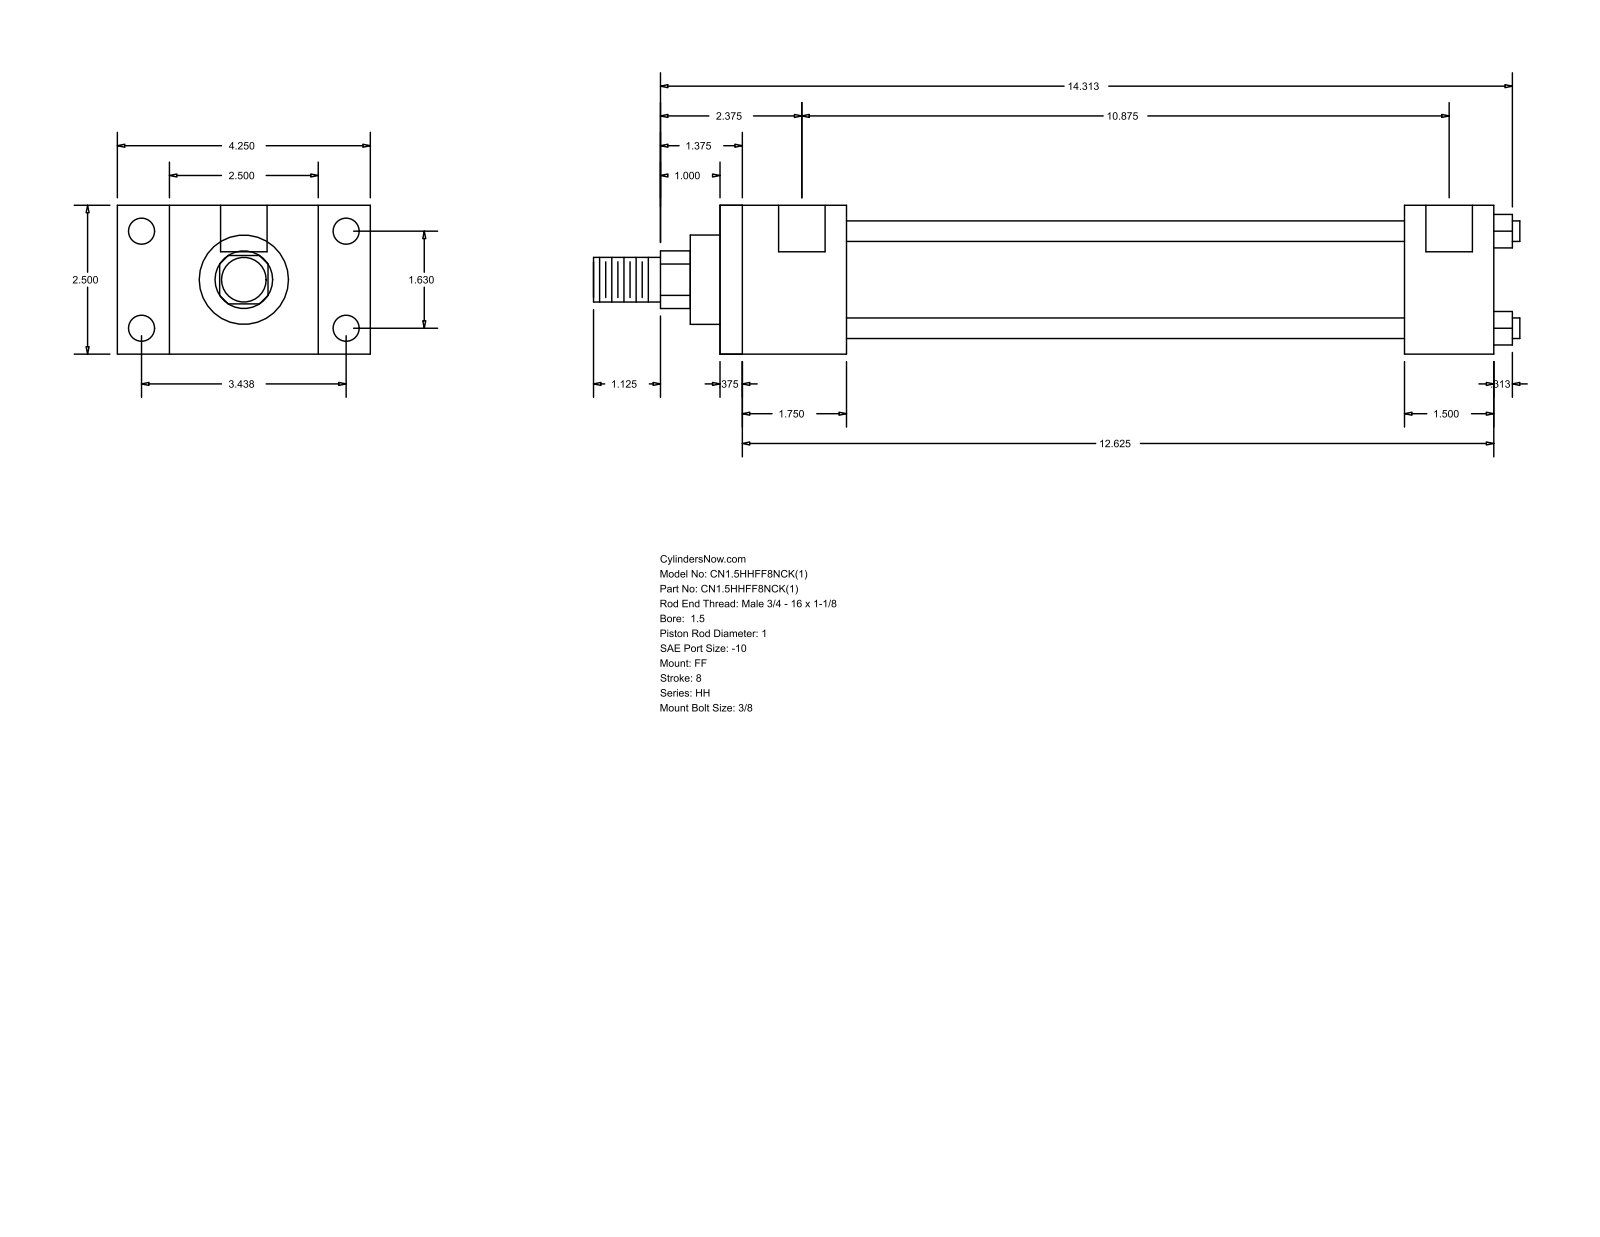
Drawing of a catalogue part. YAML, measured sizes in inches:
part_name: "HH_FF__0150_1"
step_written_by: "GSSL Pune (CONFIG_CONTROL_DESIGN)"
units: inches
bodies: {solids: 0, faces: 92, planar: 64, cylindrical: 28, other: 0}
overall_size: [15.563, 4.25, 2.5]
round_holes:
  - {diameter: 0.219, count: 4}
  - {diameter: 0.438, count: 4}
  - {diameter: 0.781, count: 2}
round_bosses_or_shafts:
  - {diameter: 0.345, count: 4}
  - {diameter: 1.75, count: 1}
  - {diameter: 1.5, count: 1}
  - {diameter: 1, count: 1}
  - {diameter: 0.75, count: 1}
partial_cylinders:
  - {radius: 0.484, count: 1}
face_to_face_distances: [2.5, 13, 0.375, 12.625, 1.5, 2.125, 1.75, 10.875, 11.5, 11.125]
hole_center_spacings: [0.063, 1.63, 3.438, 3.805, 10.937, 11, 10.875]
